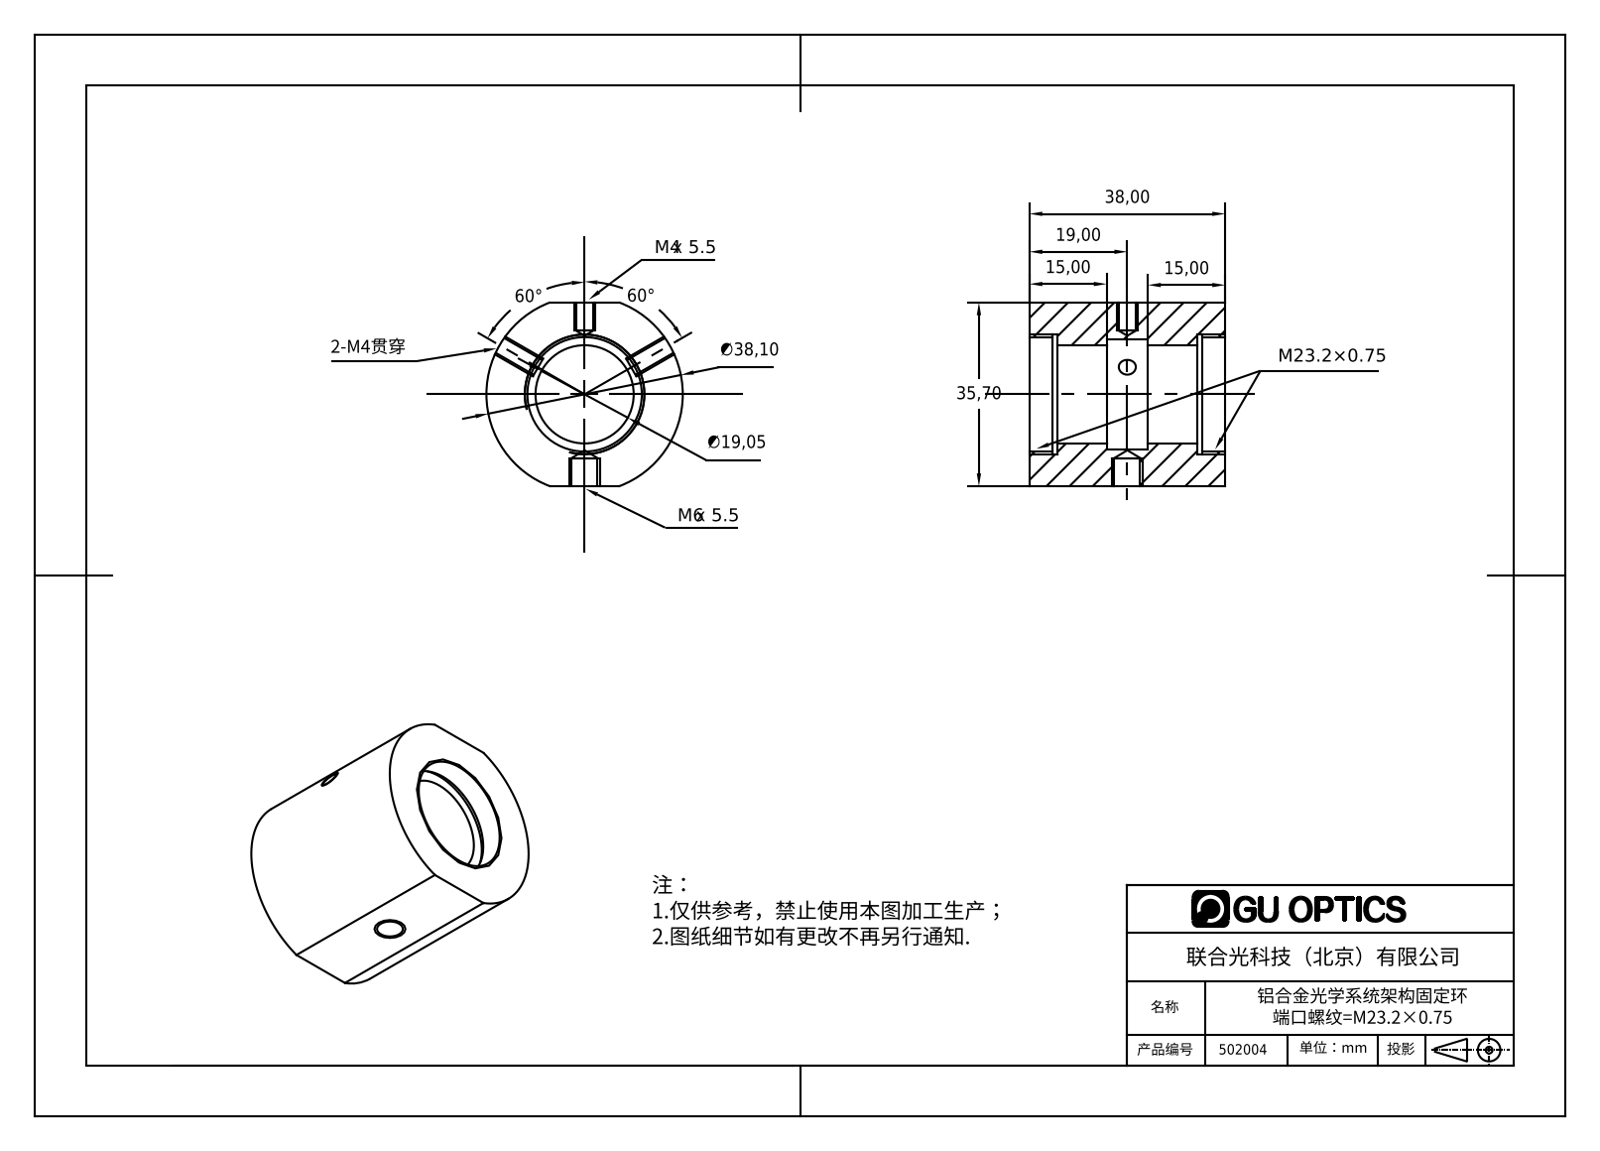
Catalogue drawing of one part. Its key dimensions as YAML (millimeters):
part_name: "502004"
step_written_by: "SolidWorks 2016 (CONFIG_CONTROL_DESIGN)"
units: millimeters
bodies: {solids: 1, faces: 39, planar: 10, cylindrical: 25, other: 4}
overall_size: [38.1, 38, 35.7]
volume: 29601
surface_area: 9240
round_holes:
  - {diameter: 3.3, count: 3}
  - {diameter: 5, count: 1}
  - {diameter: 19.05, count: 1}
  - {diameter: 21.25, count: 1}
  - {diameter: 22.2, count: 1}
  - {diameter: 23.4, count: 1}
partial_cylinders:
  - {radius: 19.05, count: 1}
face_to_face_distances: [38, 35.7, 5.5, 32.5, 27, 15, 23, 9.5, 17.5, 4.5]
